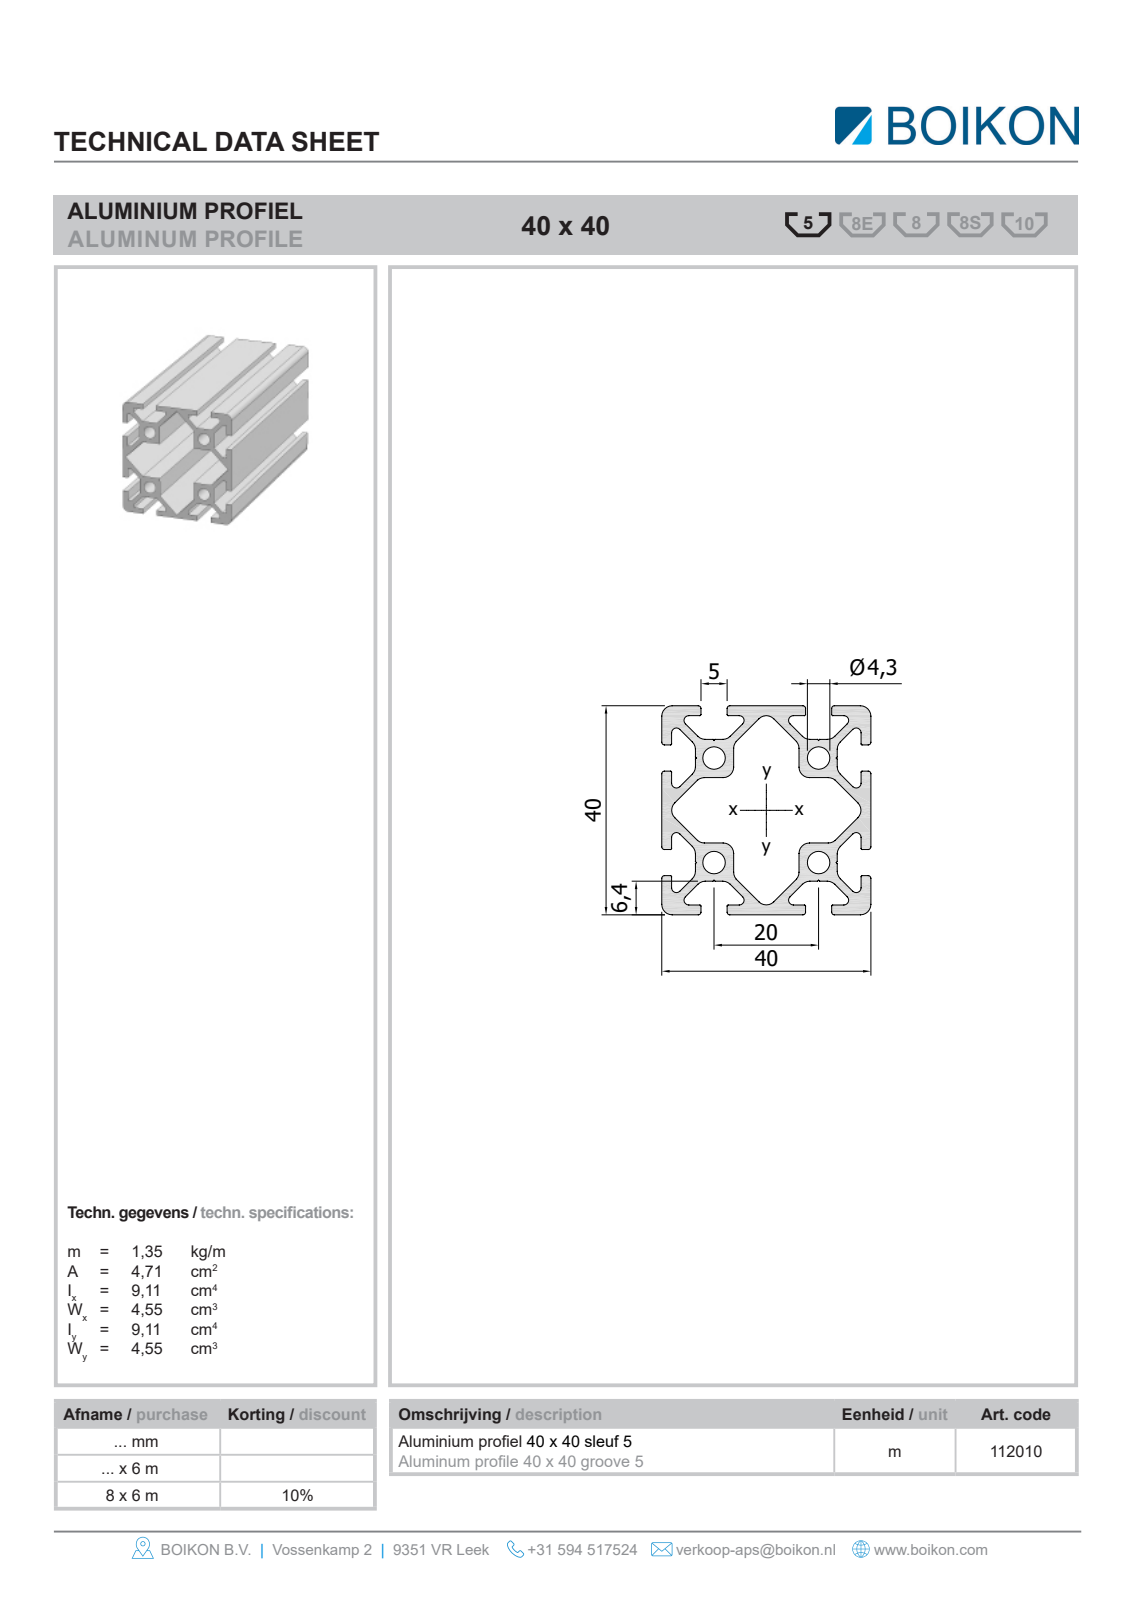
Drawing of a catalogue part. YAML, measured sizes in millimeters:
part_name: "Root; 11201040x40BOIKON0"
step_written_by: "HiCAD 2013 1802.4 Build 509 (AUTOMOTIVE_DESIGN)"
units: millimeters
bodies: {solids: 1, faces: 110, planar: 102, cylindrical: 8, other: 0}
overall_size: [1000, 40, 40]
volume: 491774
surface_area: 510353
round_holes:
  - {diameter: 4.3, count: 4}
partial_cylinders:
  - {radius: 2, count: 4}
face_to_face_distances: [14.14, 20, 1.5, 1.8, 38.2, 40, 13.7, 26.3, 11.9, 24.5]
hole_center_spacings: [20, 28.28]
